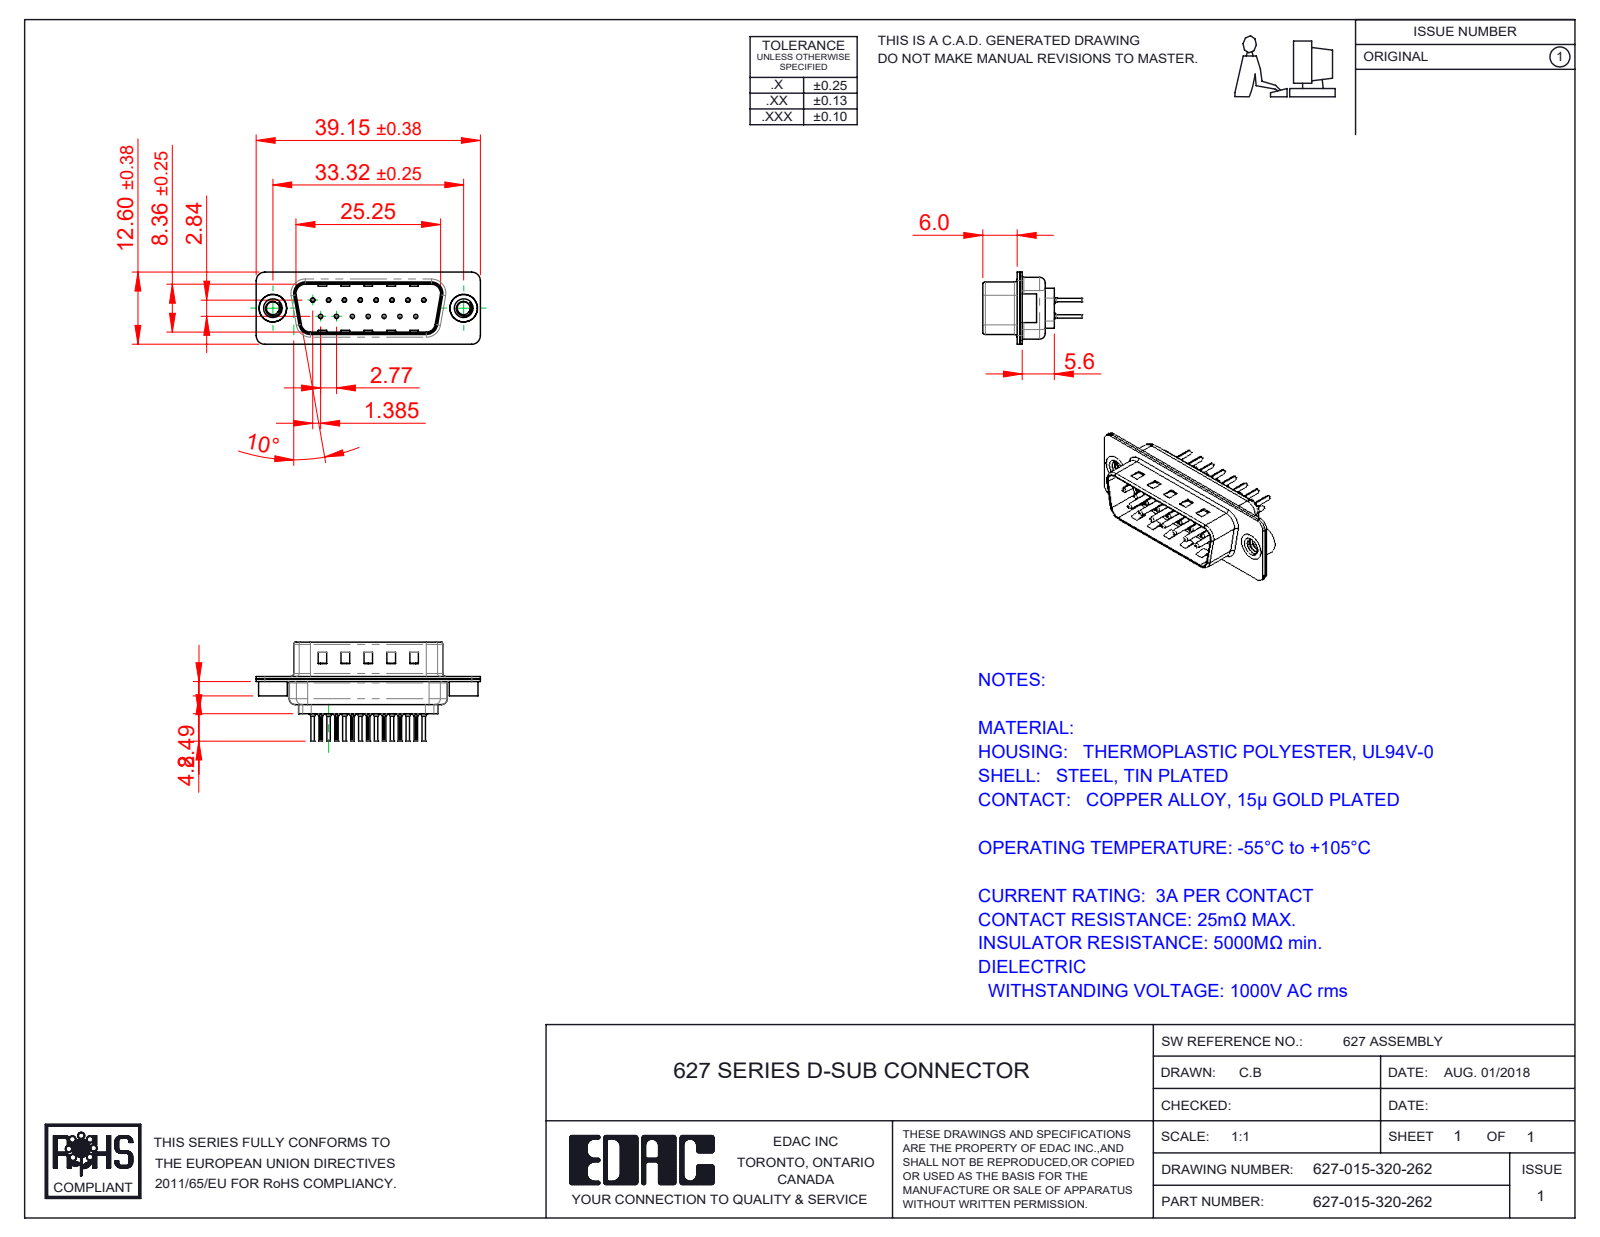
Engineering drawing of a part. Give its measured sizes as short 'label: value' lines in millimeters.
name: 627 Contact Row 2_20L; 627 Shell Rear_15 Contacts; 627 Housing_15 LP; 627 Shell Front_15 Contacts (+3 more)
written by: SolidWorks 2020 (CONFIG_CONTROL_DESIGN)
unit: mm
bodies: 20 solids, 1806 faces (499 planar, 686 cylindrical, 621 other)
size: 39.15 × 17.3 × 12.6
volume: 1 826 mm³; area: 5 382 mm²
holes: 15× ⌀0.2, 15× ⌀0.35, 15× ⌀1.1, 15× ⌀1.6, 2× ⌀2.26, 2× ⌀4, 2× ⌀4.8
bosses: 15× ⌀2, 15× ⌀1.5, 15× ⌀0.75, 15× ⌀0.6, 2× ⌀5, 2× ⌀4.9
rounds: 30× R0.1, 16× R1.5, 12× R2, 8× R0.5, 8× R1.6, 4× R0.25, 4× R0.6, 4× R0.65
face distances: 0.4, 0.45, 0.9, 0.82, 9.58, 8.76, 1.5, 1.4, 6.5, 5.6
hole spacings: 3.16, 2.77, 5.54, 8.31, 11.08, 5.03, 5.04, 7.48
